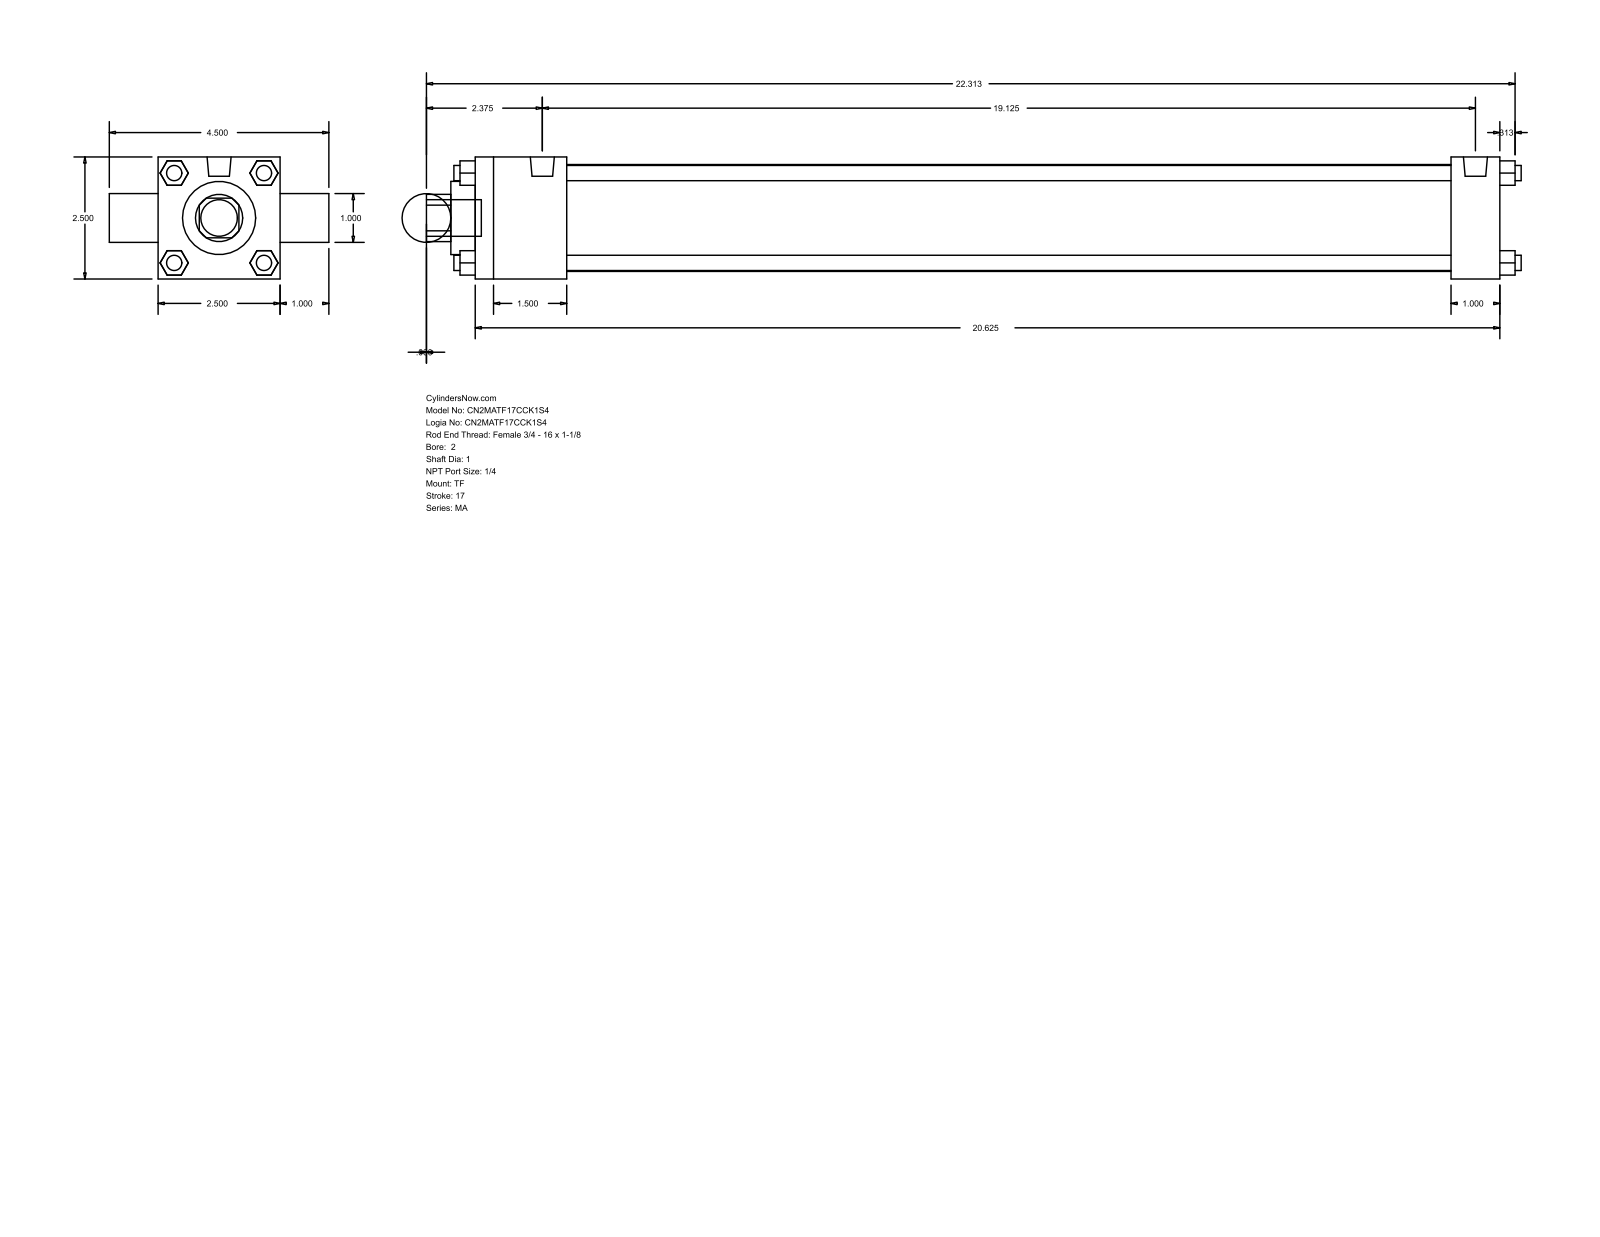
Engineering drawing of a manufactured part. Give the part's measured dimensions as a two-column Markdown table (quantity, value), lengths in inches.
| quantity | value |
| --- | --- |
| part name | MA_TF__0200_1 |
| STEP written by | GSSL Pune (CONFIG_CONTROL_DESIGN) |
| units | inches |
| bodies | 0 solids, 120 faces (92 planar, 28 cylindrical, 0 other) |
| overall size | 22.437 × 4.5 × 2.5 |
| round holes (diameter × count) | 1 × 2, 1.5 × 1, 2.19 × 1 |
| round bosses / shafts (diameter × count) | 0.313 × 7, 0.492 × 2, 0.75 × 1 |
| partial cylindrical surfaces (radius × count) | 0.484 × 1 |
| main face-to-face distances | 2.5, 1, 21, 0.5, 1.875, 20, 18.125, 19.125, 3.5, 1.593 |
